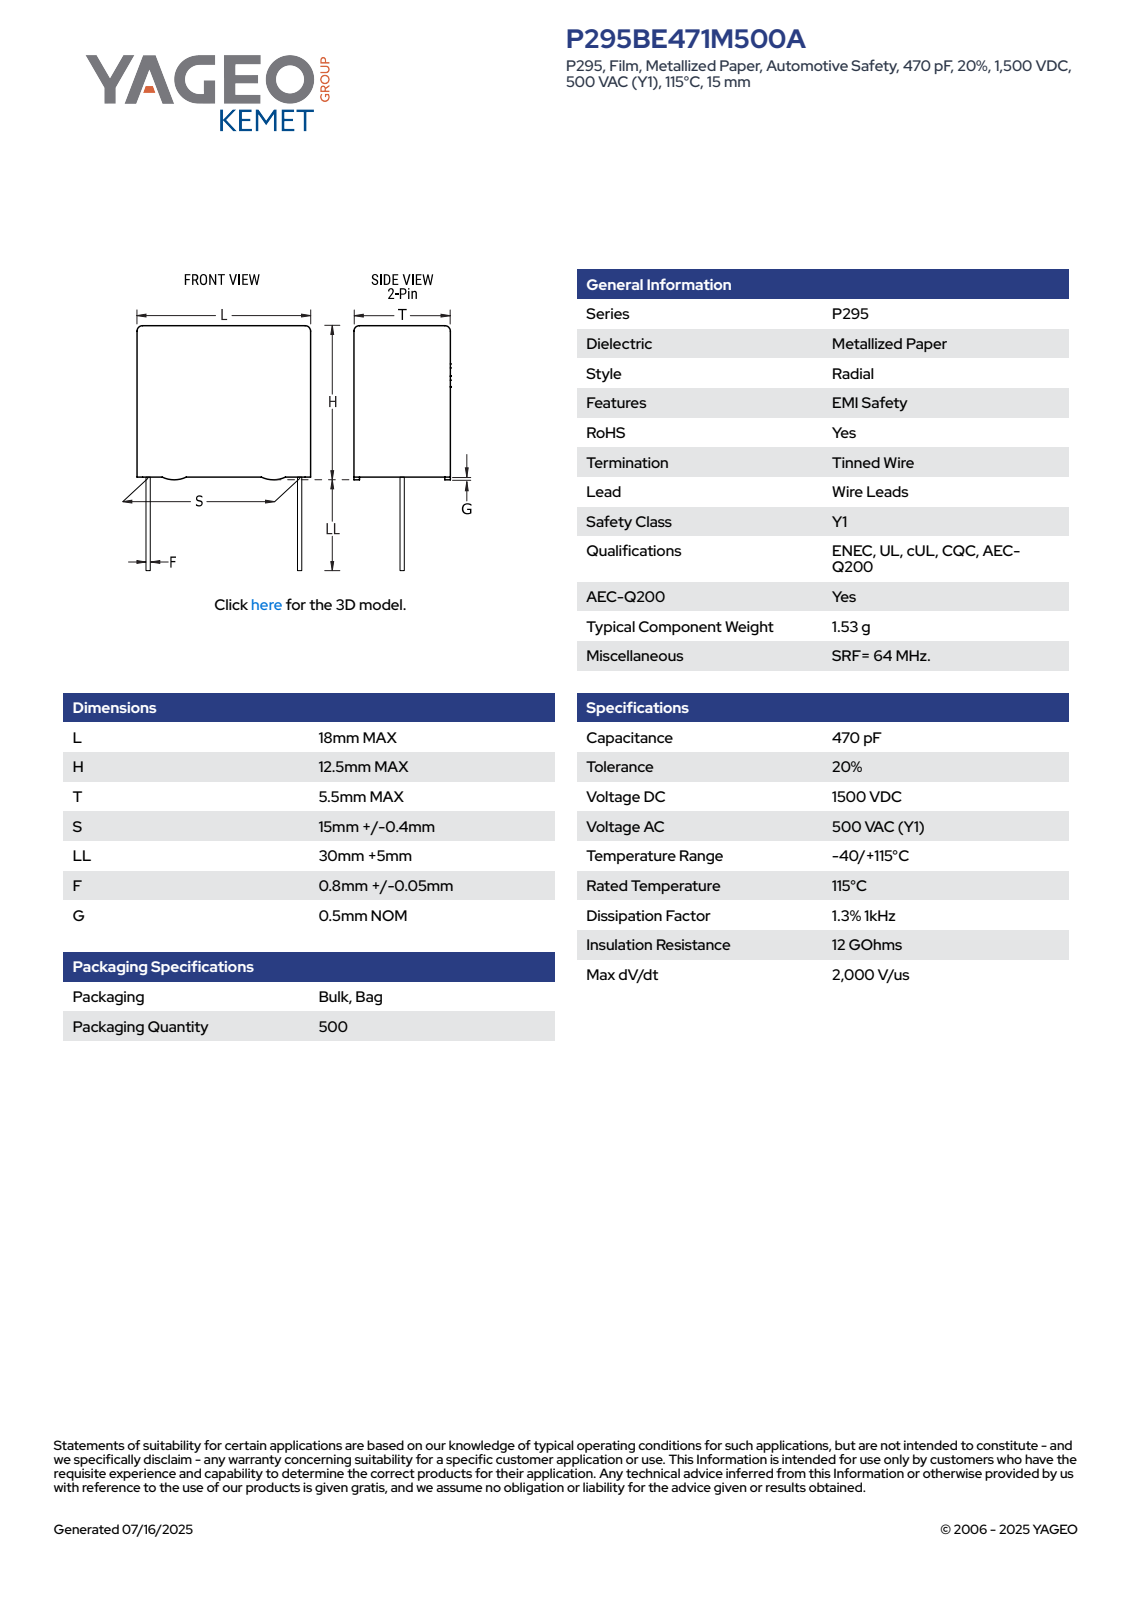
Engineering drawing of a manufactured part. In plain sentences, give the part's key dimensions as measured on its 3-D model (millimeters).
The part is named "CFR_RBG_18X12.5X5.5_L18H12.5T5.5S15LL35F0.85G0.5". Its 3-D file was written by "SolidWorks 2014 (AUTOMOTIVE_DESIGN)". It is 4 solids with 89 faces: 81 planar, 8 cylindrical and 0 other. Overall it measures 47.5 by 18 by 5.5 millimeters. Its volume is 1 228 cubic millimeters and its surface area 989 square millimeters. Round bosses or shafts: 2 of diameter 0.85. Partial cylindrical surfaces (rounded edges, fillets, slot ends): 4 of radius 0.5. The main face-to-face distances are 5.5, 12, 18, 0.31, 5.19, 0.5, 12.5, 4.88, 35, 35.5.
